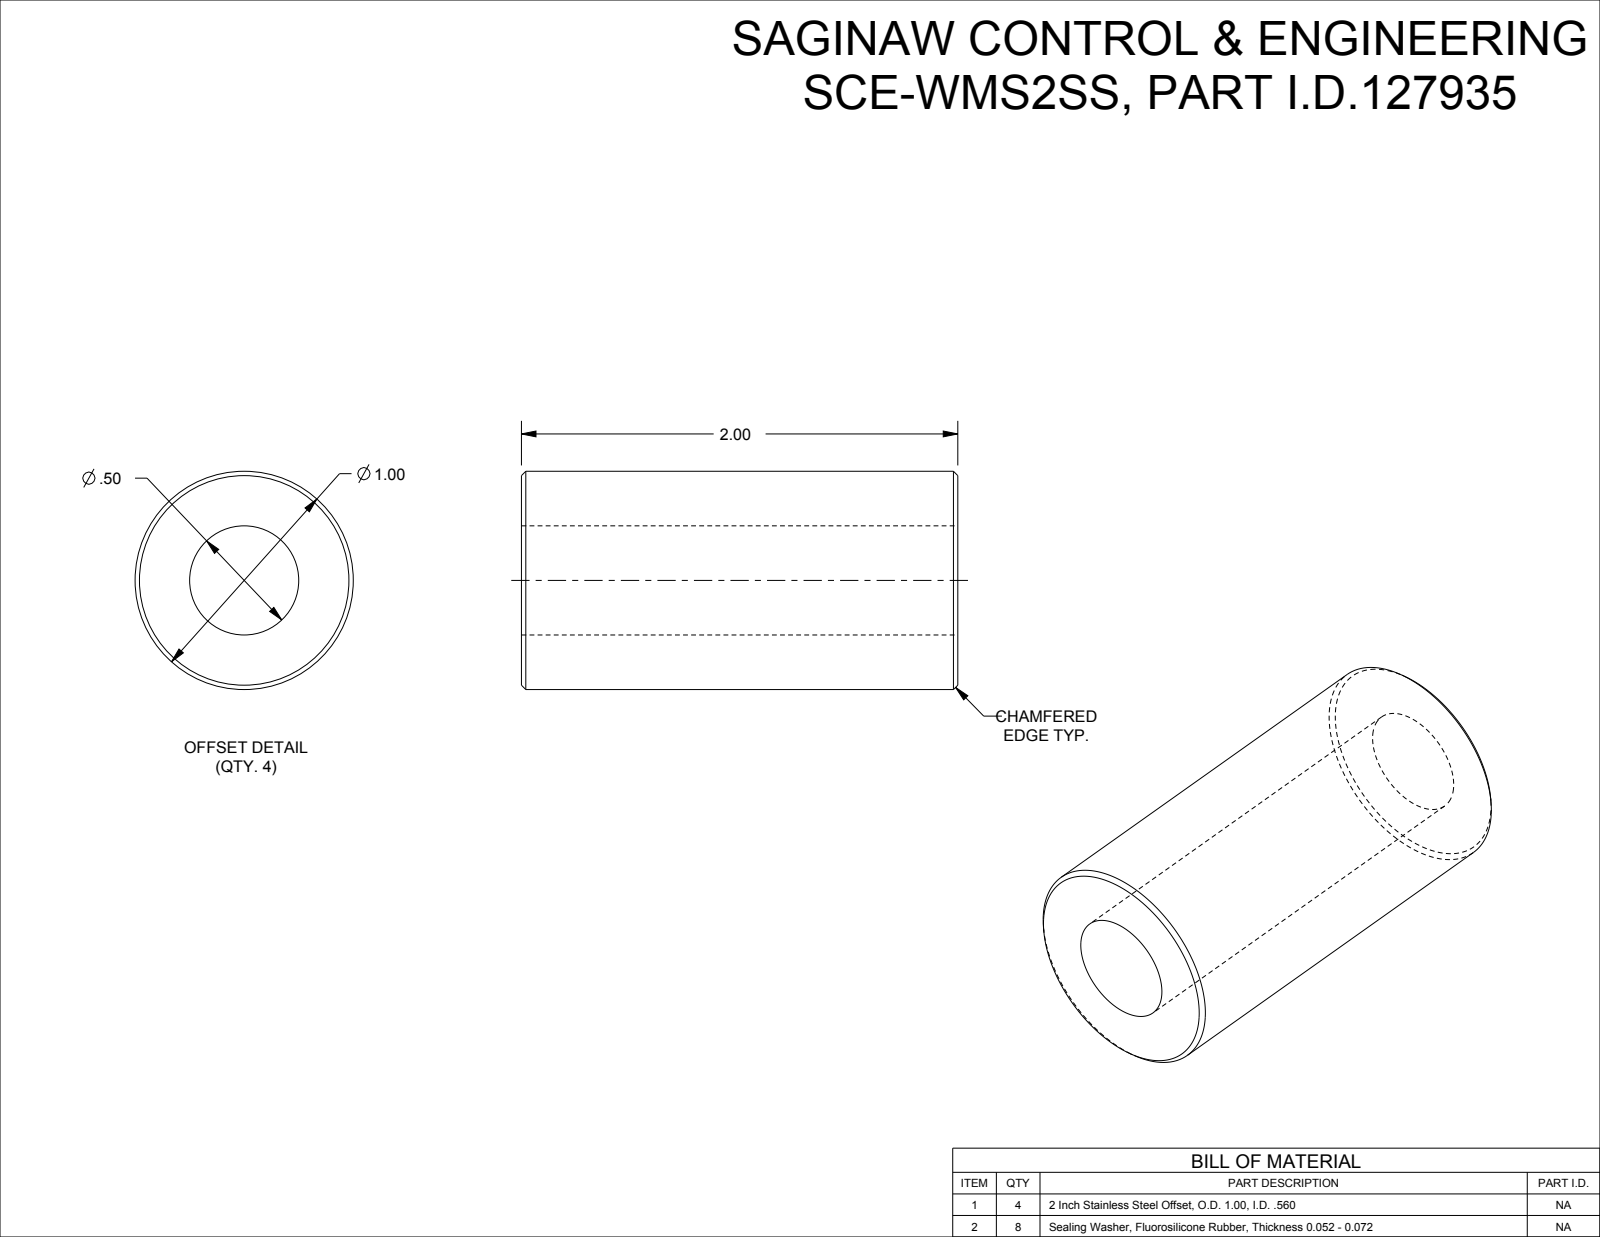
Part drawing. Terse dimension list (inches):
name: SCE-WMS2SS
written by: SolidWorks 2019 (CONFIG_CONTROL_DESIGN)
unit: in
bodies: 3 solids, 14 faces (6 planar, 6 cylindrical, 2 other)
size: 2.124 × 1 × 1
volume: 1.229 in³; area: 12.66 in²
holes: 1× ⌀0.355, 1× ⌀0.5
bosses: 1× ⌀1, 1× ⌀0.812
face distances: 2, 0.062, 2.062, 2.124
